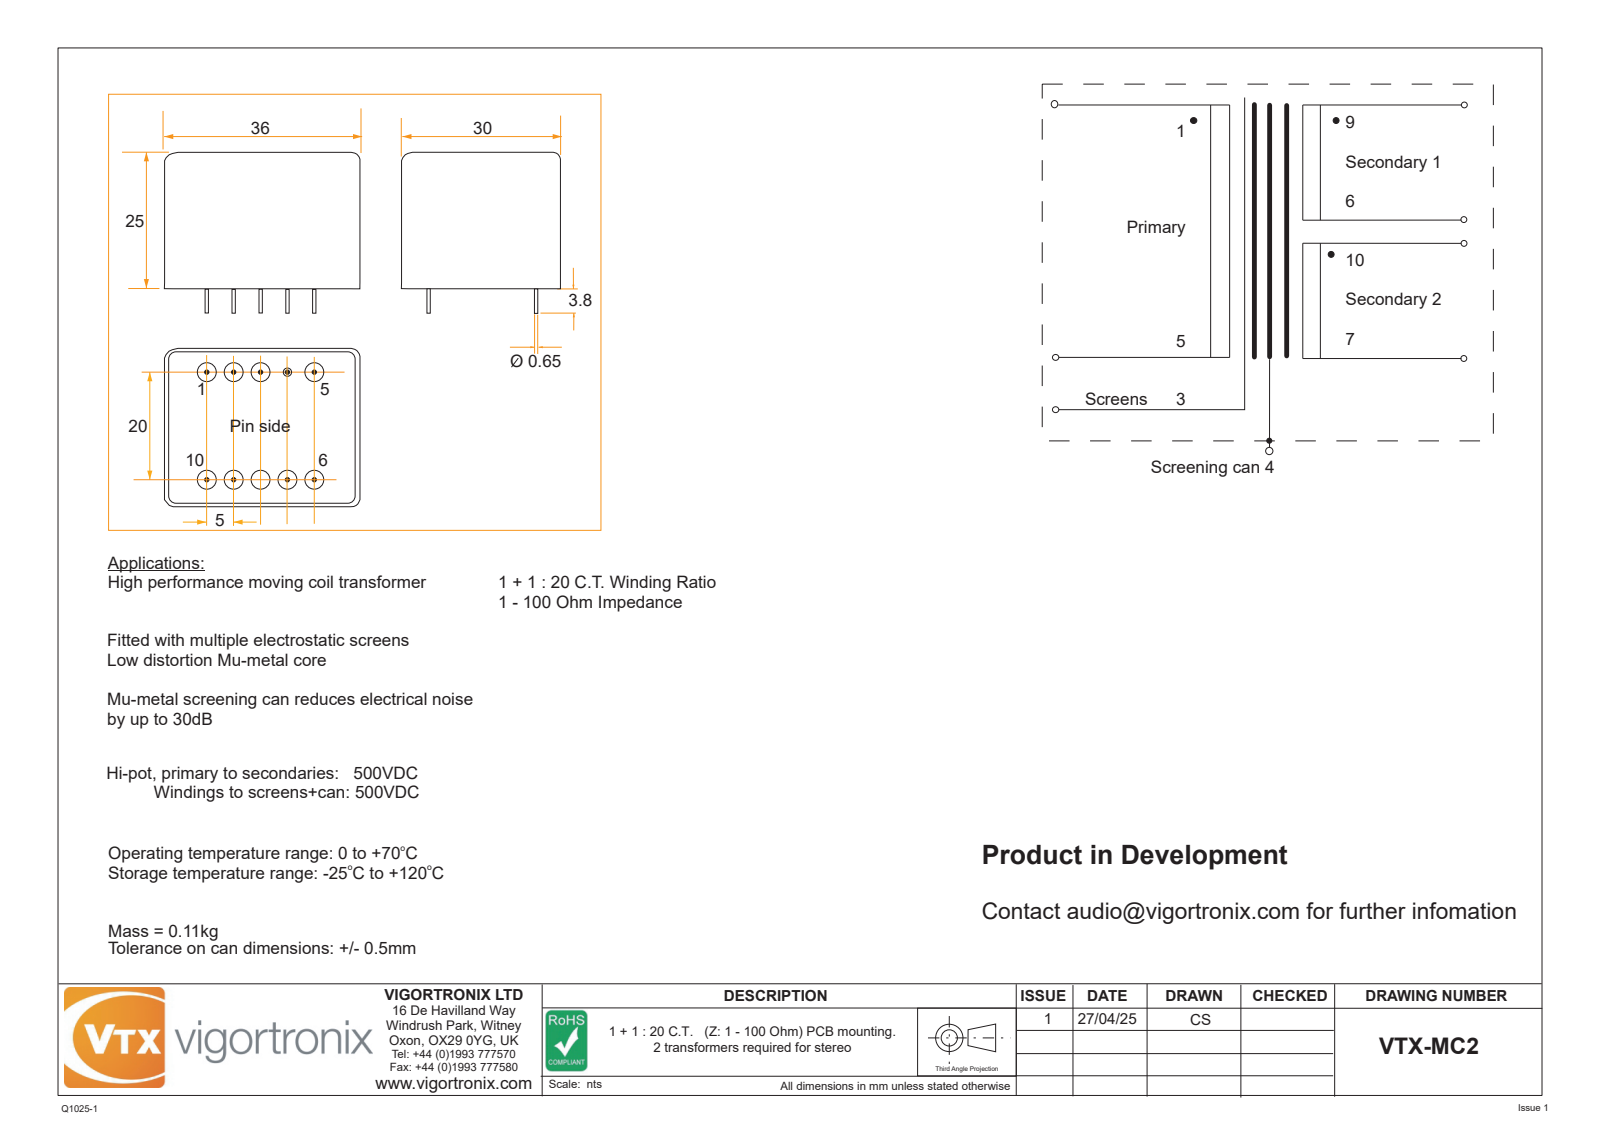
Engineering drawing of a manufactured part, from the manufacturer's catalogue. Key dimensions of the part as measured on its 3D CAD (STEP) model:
Part name (STEP PRODUCT): VTX-MC2 BOBBIN; VTX-MC2; VTX-MC2 Can; VTX-MC2 Lid
STEP written by: SolidWorks 2024 (AUTOMOTIVE_DESIGN)
Units: millimetres
Bodies: 3 solids, 104 faces (30 planar, 62 cylindrical, 12 other)
Overall size (bounding box): 36 × 30 × 28.8
Volume: 20 331 mm³ · Surface area: 13 933 mm²
Round holes (diameter × count): ⌀2.4 ×9, ⌀1.5 ×1
Round bosses / shafts (diameter × count): ⌀0.65 ×7
Partial cylindrical surfaces — rounded edges, fillets, slot ends (radius × count): R1 ×8, R2.3 ×8, R3 ×8, R2.5 ×4
Main face-to-face distances: 0.7, 0.5, 3.2, 2.7, 23.2, 22.7, 20, 1.1, 24.3, 23.8
Hole centre spacings: 5, 20.62, 20, 10, 22.36, 15, 25, 28.28
